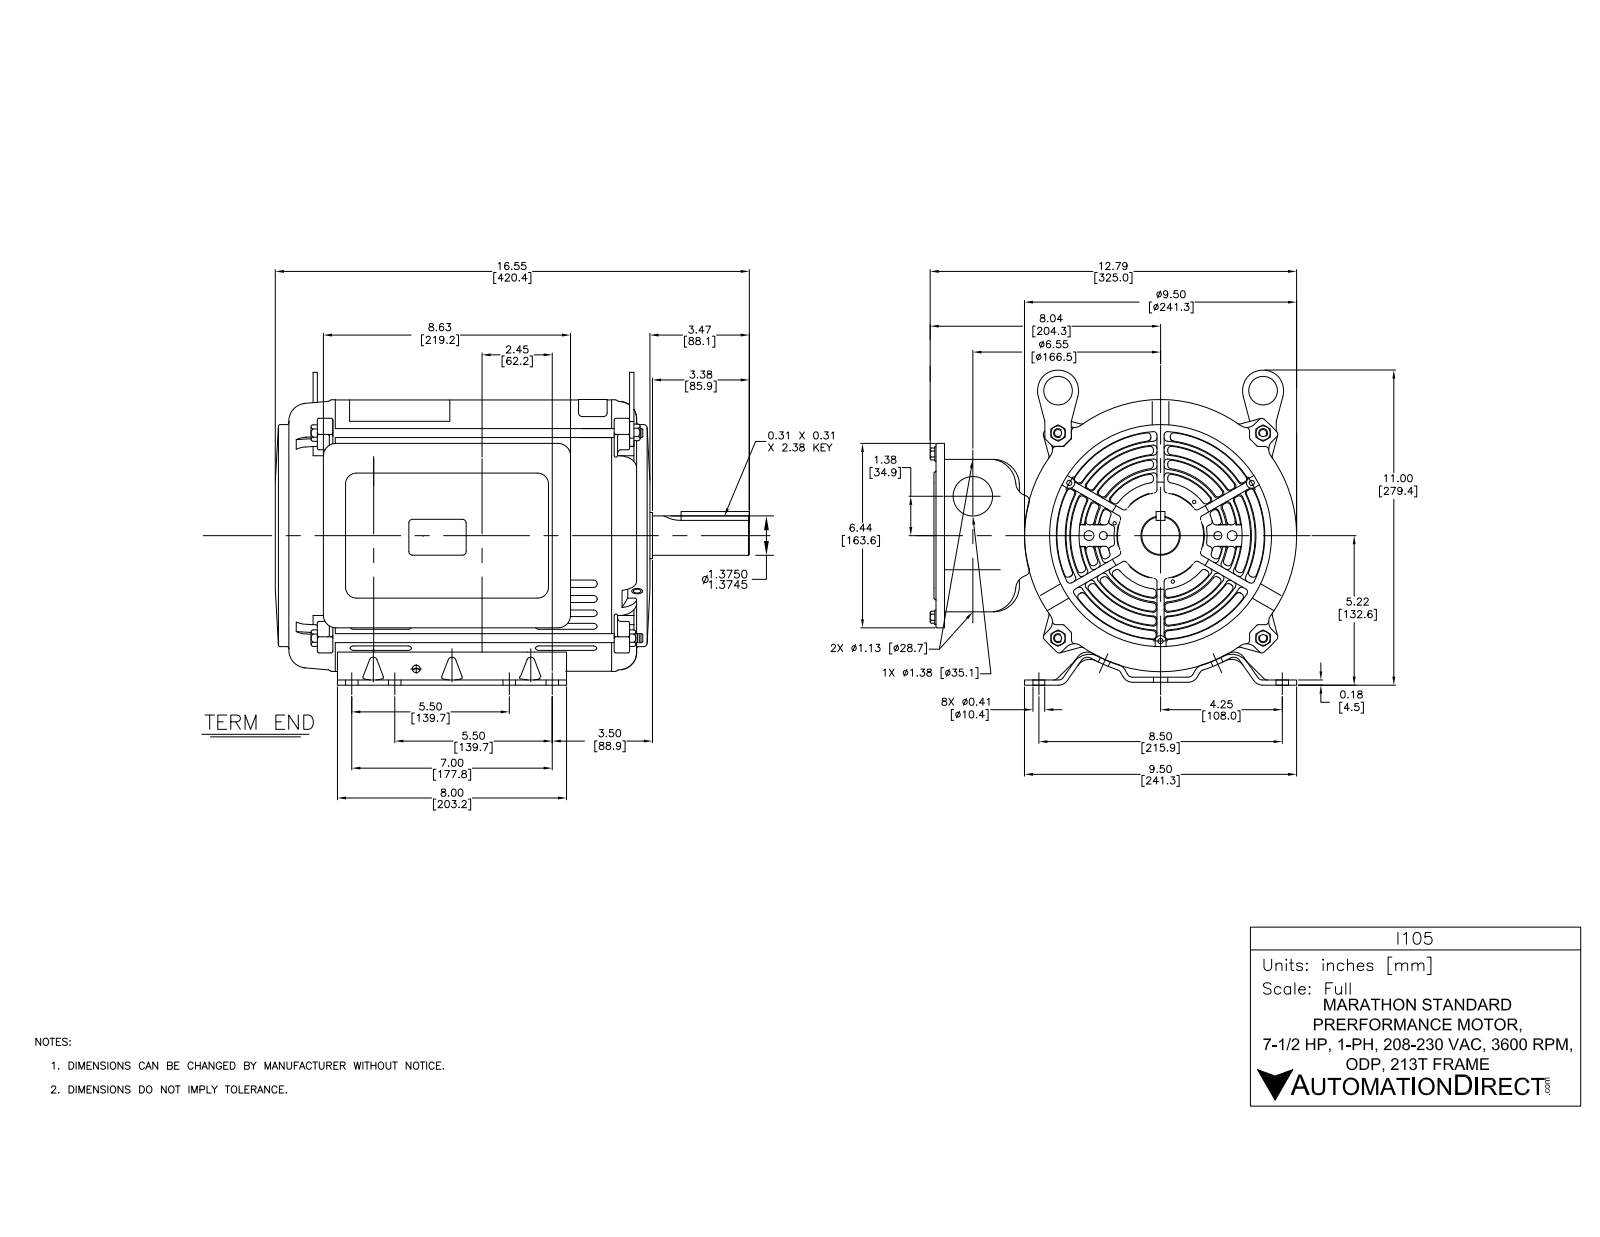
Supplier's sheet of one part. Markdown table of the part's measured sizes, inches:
| quantity | value |
| --- | --- |
| part name | I105 037642-965_Rev002 B1 |
| STEP written by | SolidWorks 2017 (AUTOMOTIVE_DESIGN) |
| units | inches |
| bodies | 35 solids, 3897 faces (1399 planar, 849 cylindrical, 1649 other) |
| overall size | 16.638 × 12.997 × 11.007 |
| volume | 151.8 in³ |
| surface area | 1 987 in² |
| round holes (diameter × count) | 0.373 × 10, 0.153 × 6, 0.219 × 6, 0.435 × 6, 0.28 × 5, 0.213 × 4, 0.257 × 4, 1 × 4, 0.125 × 3, 0.175 × 3, 0.3 × 3, 0.1 × 2 |
| round bosses / shafts (diameter × count) | 0.25 × 7, 0.52 × 5, 0.331 × 4, 0.31 × 4, 0.68 × 2, 0.5 × 2, 0.38 × 2, 0.35 × 2 |
| partial cylindrical surfaces (radius × count) | 0.135 × 72, 0.03 × 48, 0.25 × 32, 0.06 × 28, 0.12 × 26, 0.19 × 14, 0.079 × 12, 0.02 × 10 |
| main face-to-face distances | 0.035, 0.075, 0.125, 0.11, 0.059, 0.235, 0.059, 0.2, 0.179, 0.179 |
| hole center spacings | 5.7, 2.5, 1, 7.156, 1.5, 3.5, 3.737, 3.911 |
